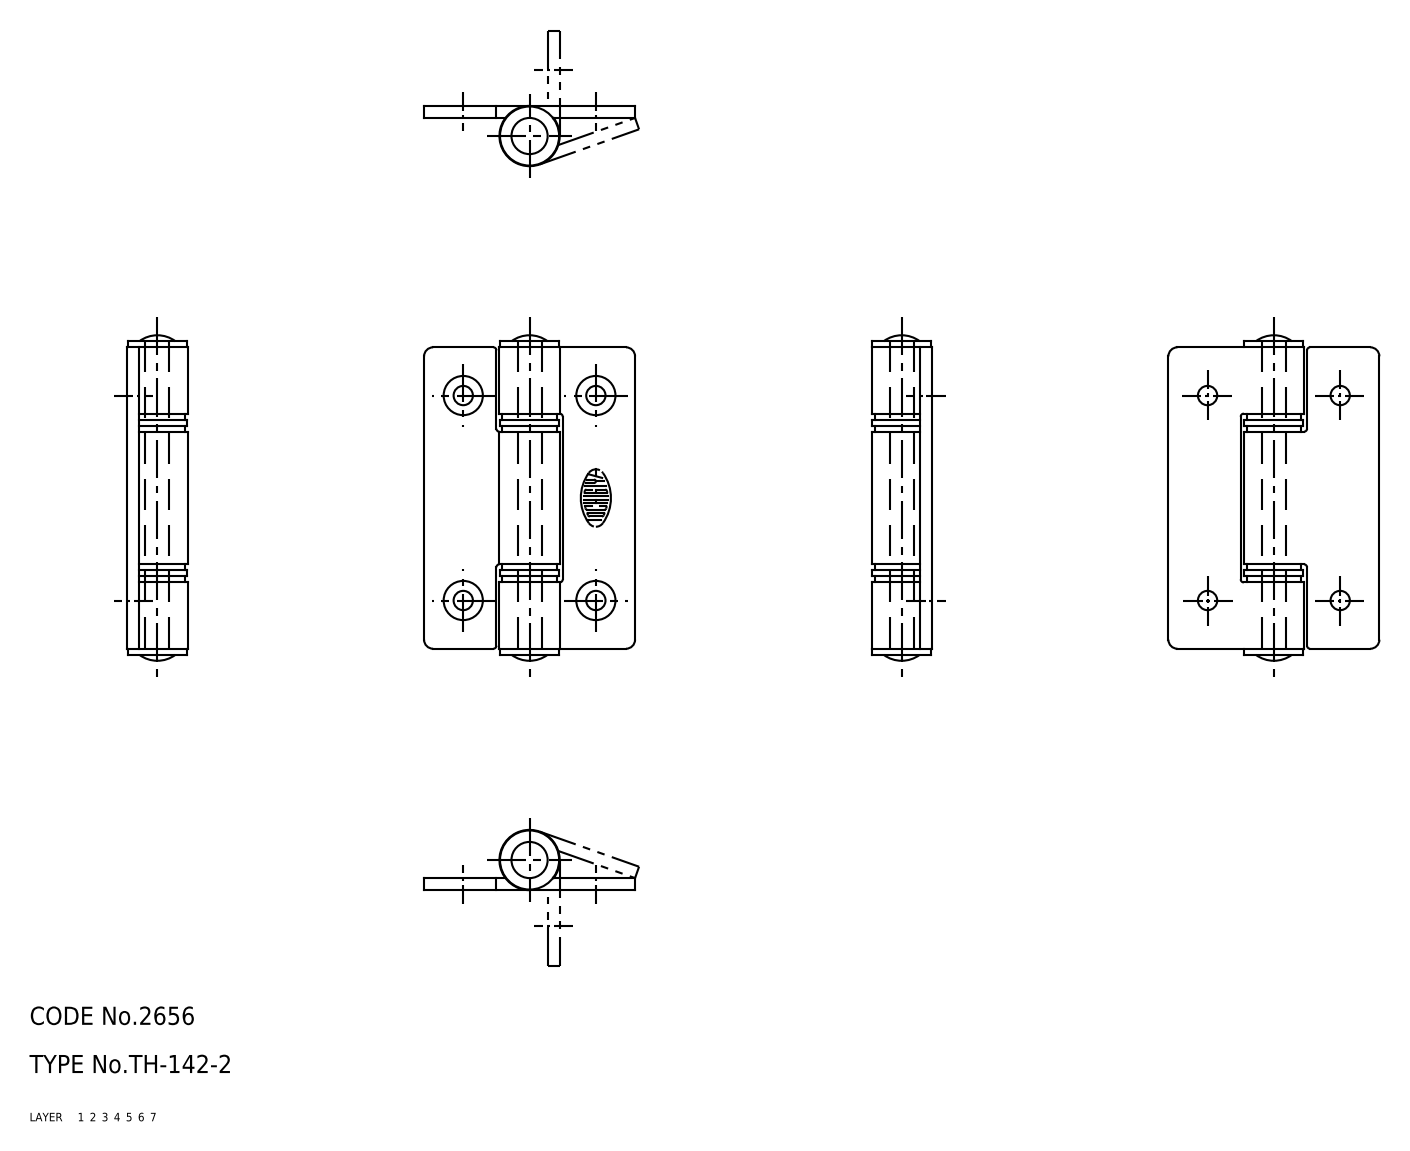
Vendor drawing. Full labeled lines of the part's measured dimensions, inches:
Part name (STEP PRODUCT): washer_A; washer; washer_B; shaft (+3 more)
STEP written by: CADfix (AUTOMOTIVE_DESIGN)
Units: inches
Bodies: 11 solids, 124 faces (0 planar, 0 cylindrical, 124 other)
Overall size (bounding box): 2.126 × 1.378 × 0.394
Volume: 0.372 in³ · Surface area: 12.82 in²
